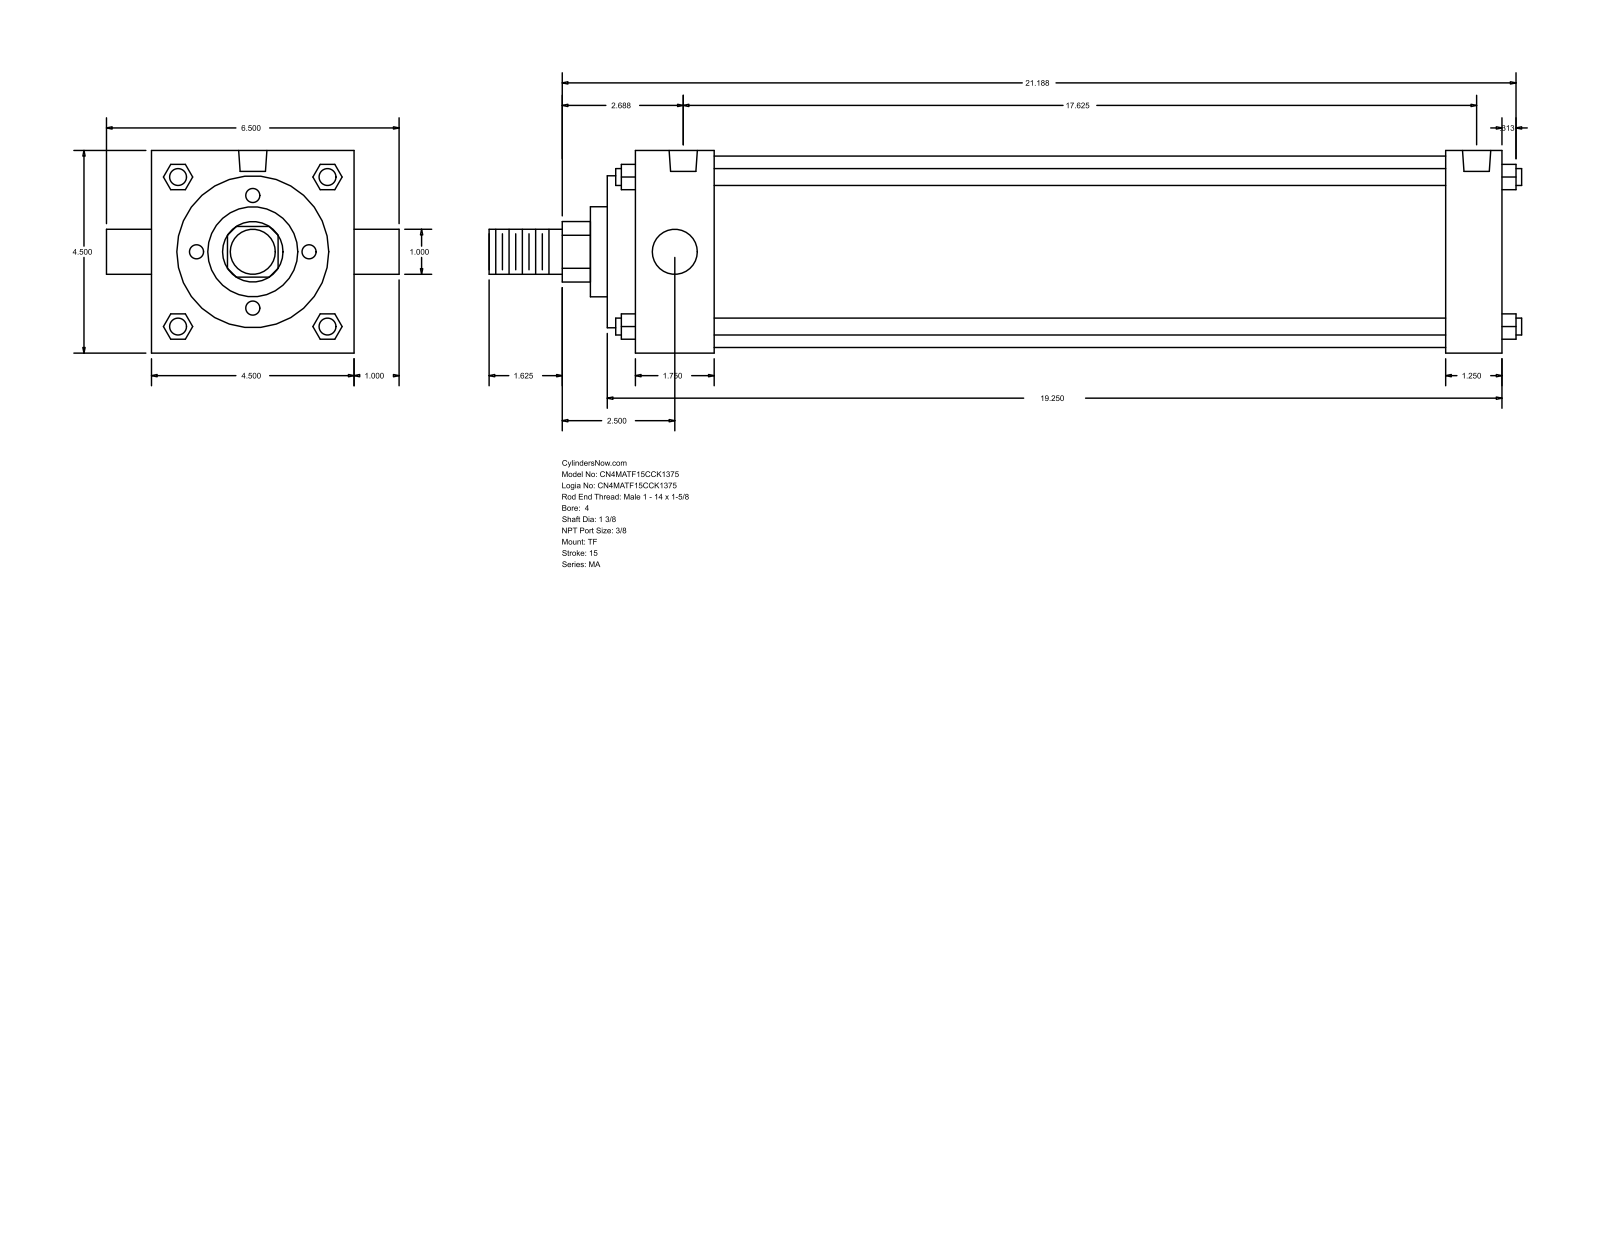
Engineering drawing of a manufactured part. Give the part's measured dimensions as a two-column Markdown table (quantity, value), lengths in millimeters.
| quantity | value |
| --- | --- |
| part name | MA_TF__0400_1.375 |
| STEP written by | GSSL Pune (CONFIG_CONTROL_DESIGN) |
| units | millimeters |
| bodies | 0 solids, 122 faces (93 planar, 29 cylindrical, 0 other) |
| overall size | 582.61 × 165.1 × 114.3 |
| round holes (diameter × count) | 11.11 × 3, 15.93 × 2 |
| round bosses / shafts (diameter × count) | 9.53 × 4, 25.4 × 2, 107.95 × 1, 85.72 × 1, 50.8 × 1, 34.92 × 1 |
| partial cylindrical surfaces (radius × count) | 17.06 × 1 |
| main face-to-face distances | 114.3, 488.96, 15.87, 504.83, 473.08, 457.21, 31.75, 60.32, 44.45, 412.76 |
| hole center spacings | 4.76, 4.77, 438.15, 442.91, 442.92, 447.68 |
